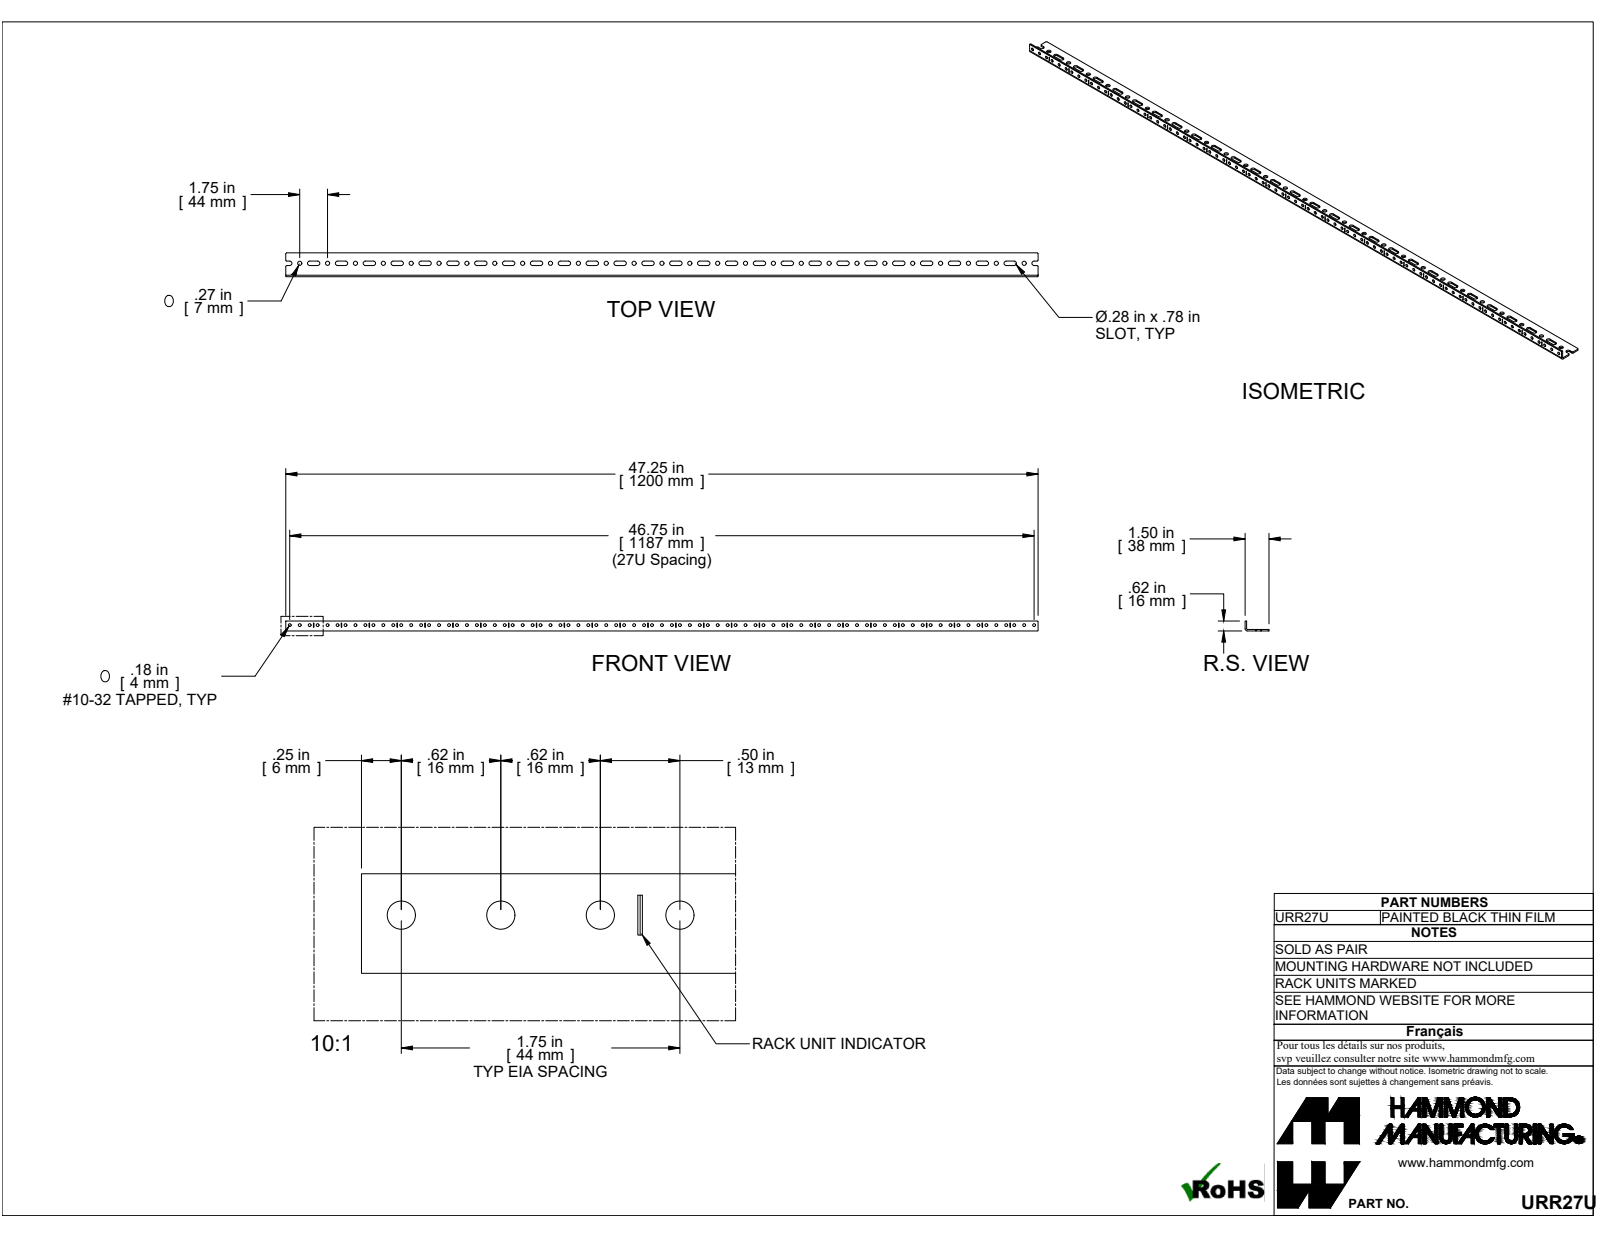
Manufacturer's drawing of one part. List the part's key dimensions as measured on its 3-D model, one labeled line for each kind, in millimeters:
Part name (STEP PRODUCT): COM57213-27
STEP written by: ST-DEVELOPER v16.7 (AUTOMOTIVE_DESIGN)
Units: millimetres
Bodies: 1 solid, 340 faces (176 planar, 164 cylindrical, 0 other)
Overall size (bounding box): 1200.15 × 38.1 × 15.88
Volume: 132 306 mm³ · Surface area: 123 075 mm²
Round holes (diameter × count): ⌀4.5 ×81, ⌀6.76 ×27
Partial cylindrical surfaces — rounded edges, fillets, slot ends (radius × count): R3.57 ×54, R1.22 ×1, R3.63 ×1
Main face-to-face distances: 2.41, 15.88, 13.47, 38.1, 35.69, 17.84, 24.98, 15.43, 22.57, 7.14
Hole centre spacings: 44.45, 177.8, 88.9, 222.25, 133.35, 266.7, 311.15, 355.6
